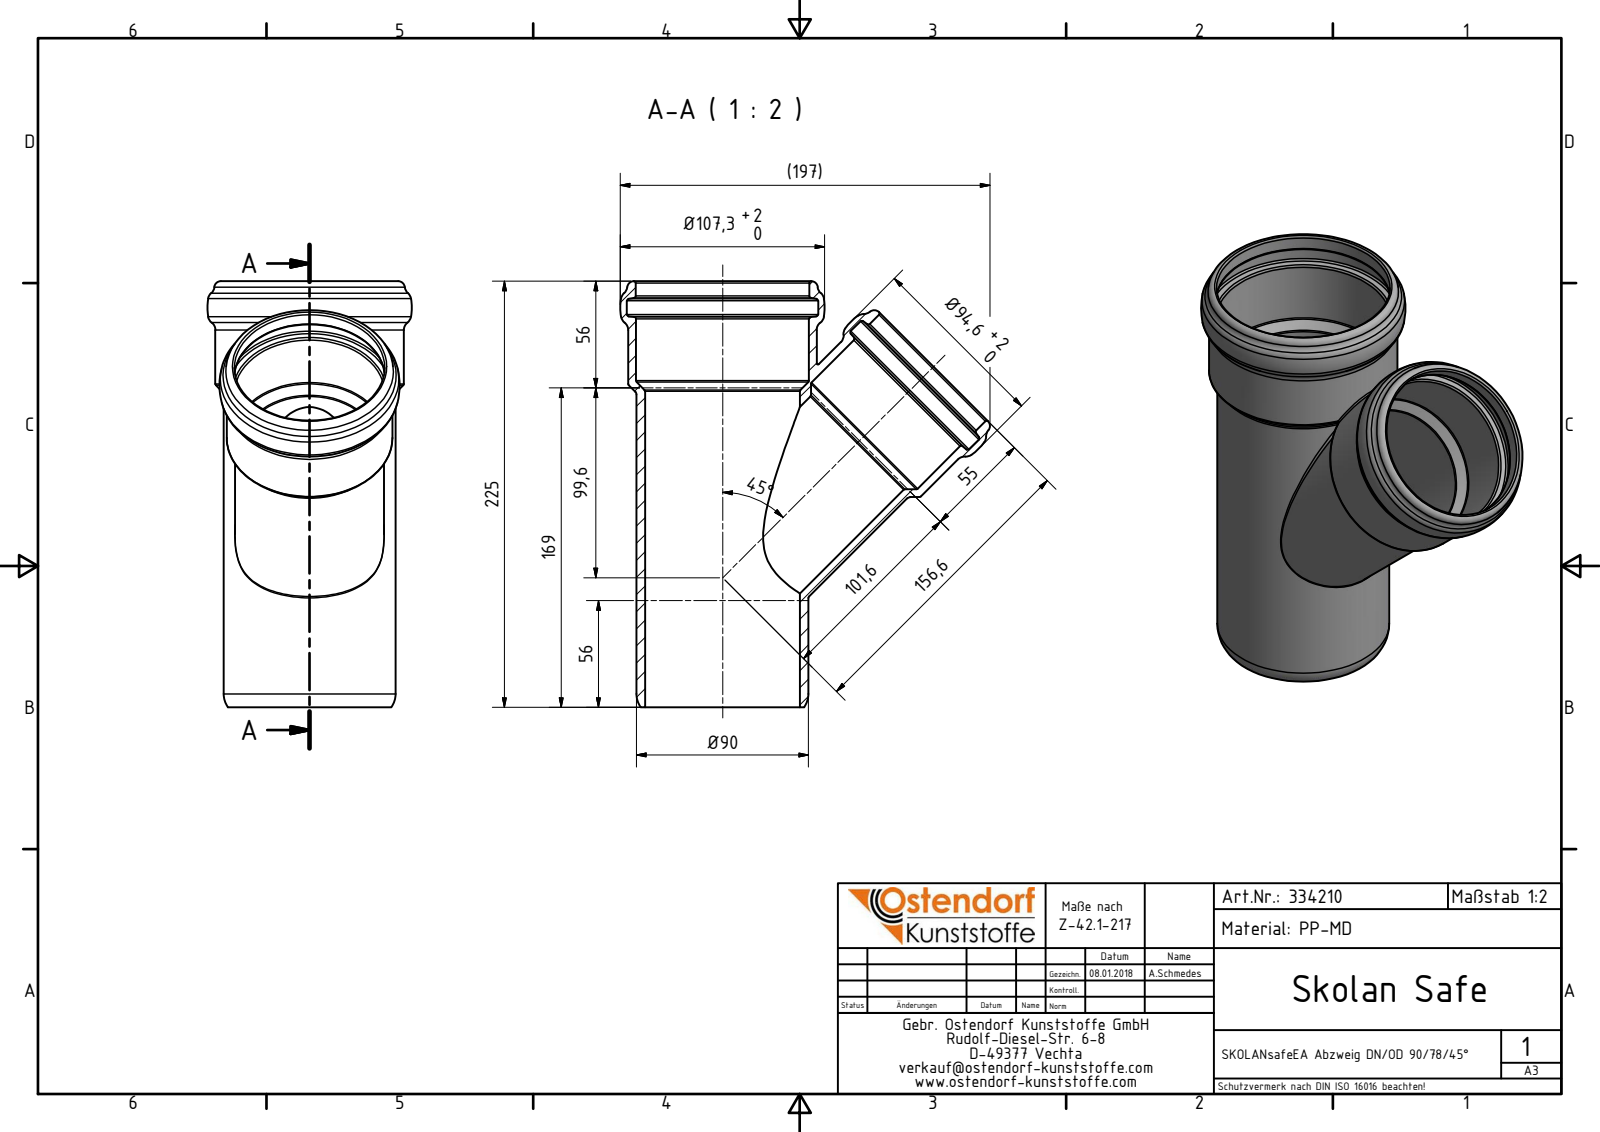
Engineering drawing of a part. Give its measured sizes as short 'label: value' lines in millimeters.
name: 334210 SKOLANsafeEA Abzweiger DN_OD 90_78_45°
written by: Autodesk Inventor 2016 (AUTOMOTIVE_DESIGN)
unit: mm
bodies: 1 solid, 64 faces (1 planar, 12 cylindrical, 51 other)
size: 223.61 × 194.1 × 107.3
volume: 366 831 mm³; area: 173 323 mm²
holes: 1× ⌀69.2, 1× ⌀78.8, 1× ⌀79, 1× ⌀81.3, 1× ⌀87.8, 1× ⌀90.8, 1× ⌀91.1, 1× ⌀100.5
bosses: 1× ⌀99, 1× ⌀90.3, 1× ⌀87, 1× ⌀78.2
